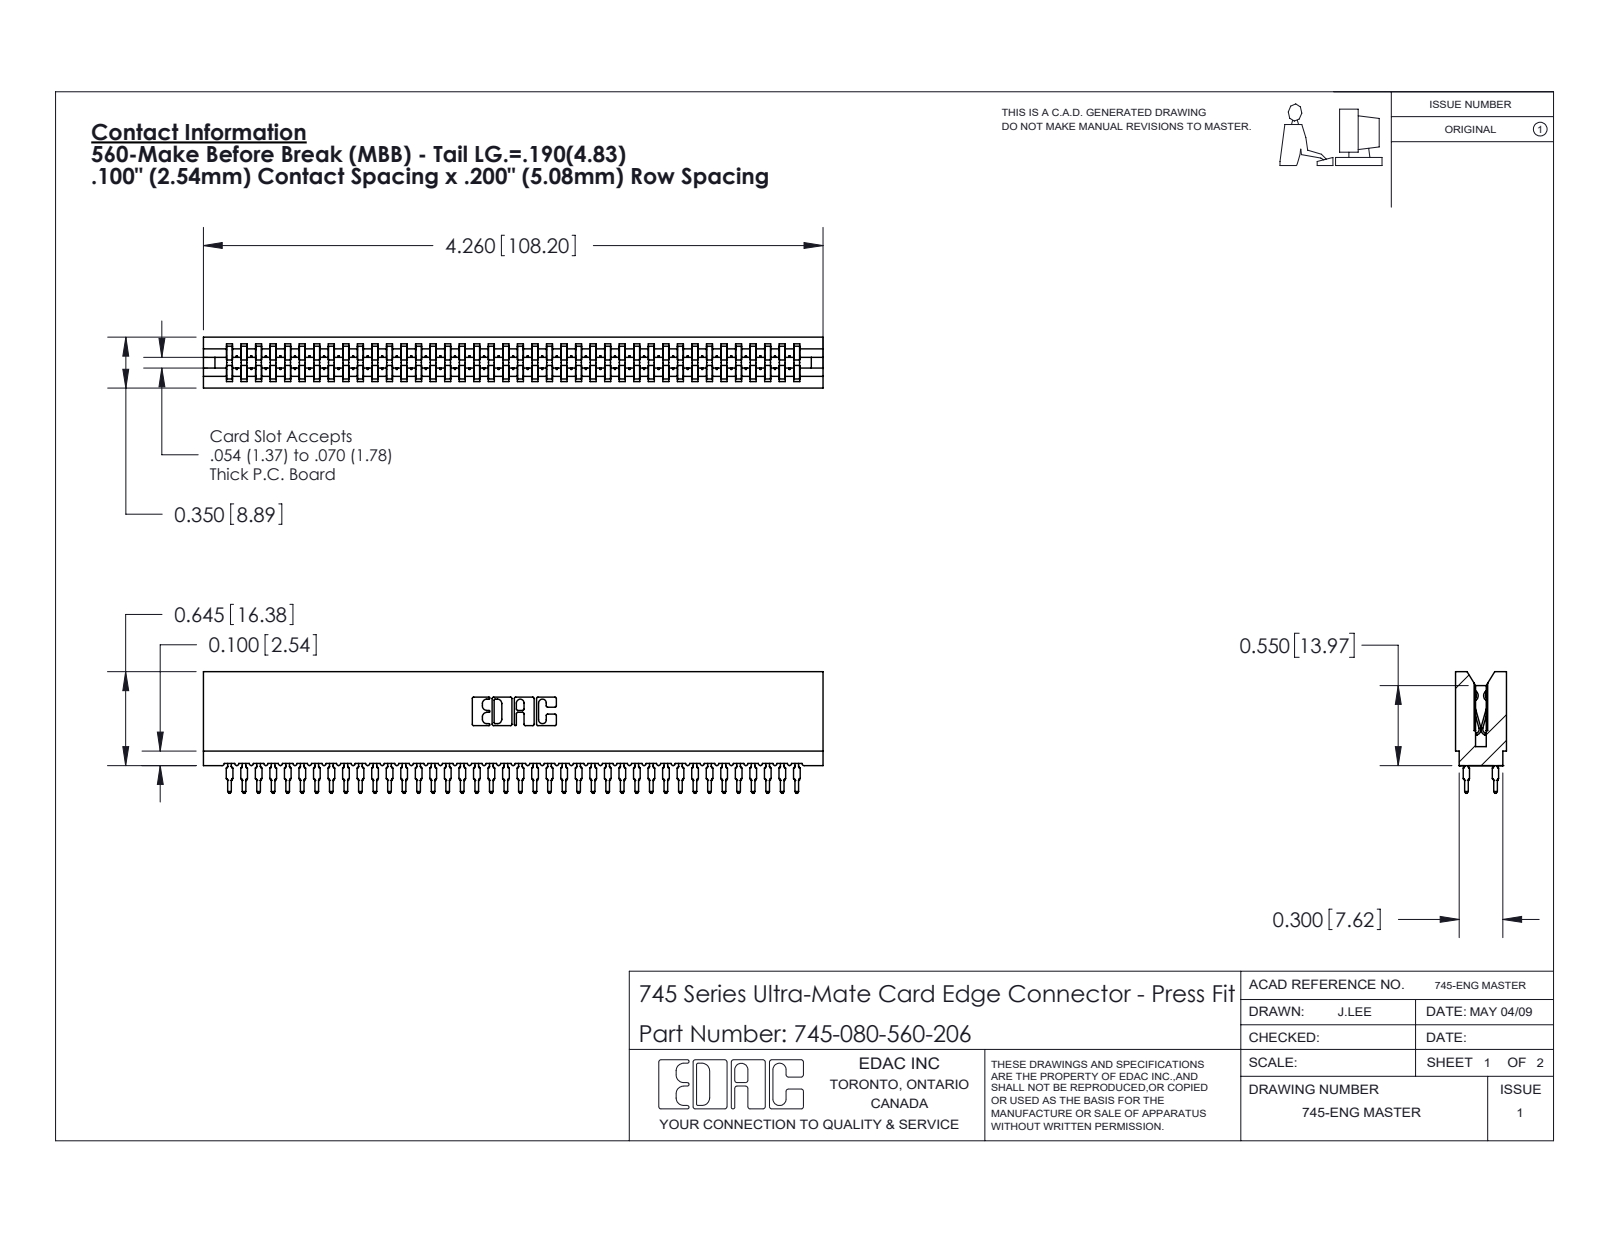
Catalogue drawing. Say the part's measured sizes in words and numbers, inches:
The part is named "745-292-001_560; 745-080-560-206; 745 Part_Insulator Option - 06". Its 3-D file was written by "SolidWorks 2020 (CONFIG_CONTROL_DESIGN)". It is 81 solids with 7976 faces: 4136 planar, 1760 cylindrical and 2080 other. Overall it measures 4.26 by 0.836 by 0.35 inches. Its volume is 0.612 cubic inches and its surface area 33.53 square inches. Partial cylindrical surfaces (rounded edges, fillets, slot ends): 160 of radius 0.021, 80 of radius 0.015, 22 of radius 0.01, 8 of radius 0.005, 8 of radius 0.011, 6 of radius 0.007, 6 of radius 0.031, 3 of radius 0.026. The main face-to-face distances are 0.35, 0.063, 0.287, 0.2, 0.138, 0.212, 0.076, 0.149, 0.045, 0.305.
